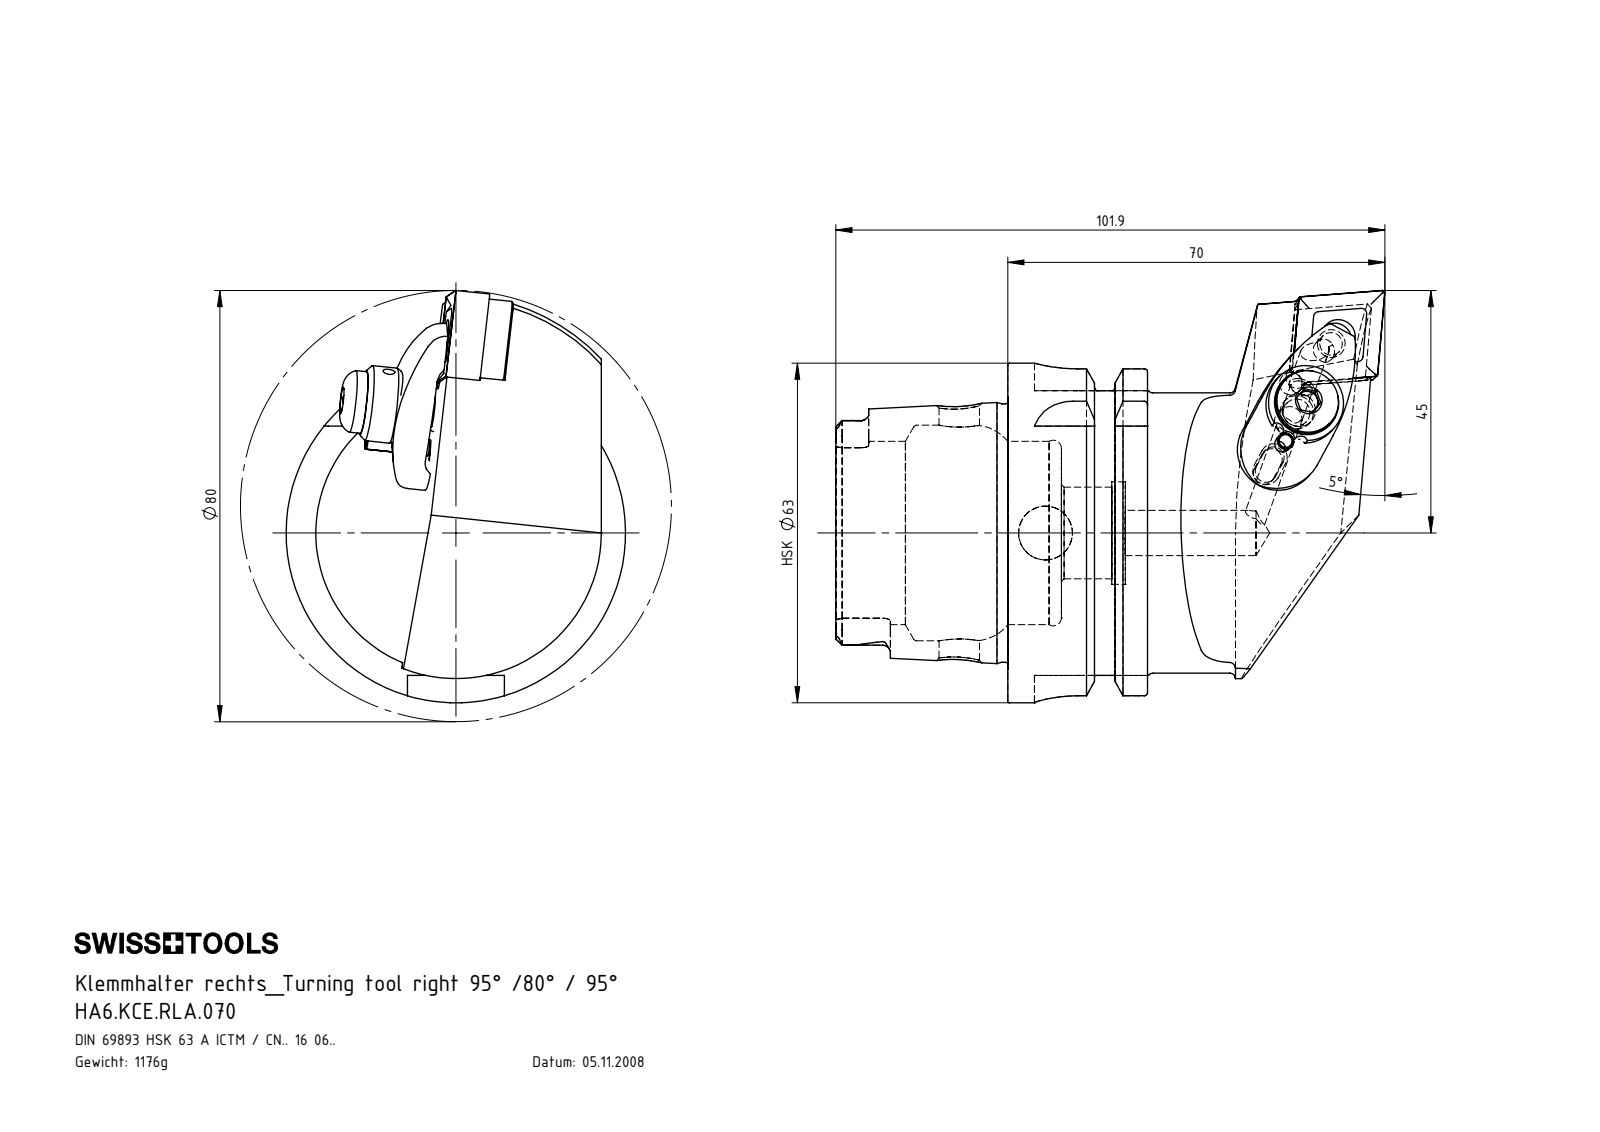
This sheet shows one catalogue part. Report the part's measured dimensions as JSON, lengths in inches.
{"part_name": "HA6-KCE.RLA.070_C; WCC-ER5.102.005_A; CNMG160604; WCE-ER2.101.004_A (+7 more)", "step_written_by": "SolidWorks 2017 (AUTOMOTIVE_DESIGN)", "units": "inches", "bodies": {"solids": 11, "faces": 464, "planar": 125, "cylindrical": 153, "other": 186}, "overall_size": [4.012, 3.012, 2.48], "volume_in3": 9.075, "surface_area_in2": 56.11, "round_holes": [[0.079, 3], [0.165, 3], [0.197, 2], [0.276, 2], [0.094, 1], [0.118, 1], [0.157, 1], [0.244, 1], [0.25, 1], [0.295, 1], [0.311, 1], [0.331, 1]], "round_bosses_or_shafts": [[0.197, 2], [0.118, 2], [2.48, 1], [2.163, 1], [2.047, 1], [1.887, 1], [0.551, 1], [0.453, 1]], "partial_cylinders_radius": [[0.018, 6], [0.055, 6], [0.016, 4], [0.031, 4], [0.039, 4], [0.315, 4], [0.059, 3], [0.031, 2]], "face_to_face_distances": [1.022, 0.63, 0.392, 1.256, 1.648, 2.278, 2.079, 0.858, 0.467, 2.114], "hole_center_spacings": [0.242, 0.315, 0.323, 0.537, 0.922, 0.235, 0.315, 0.315]}
